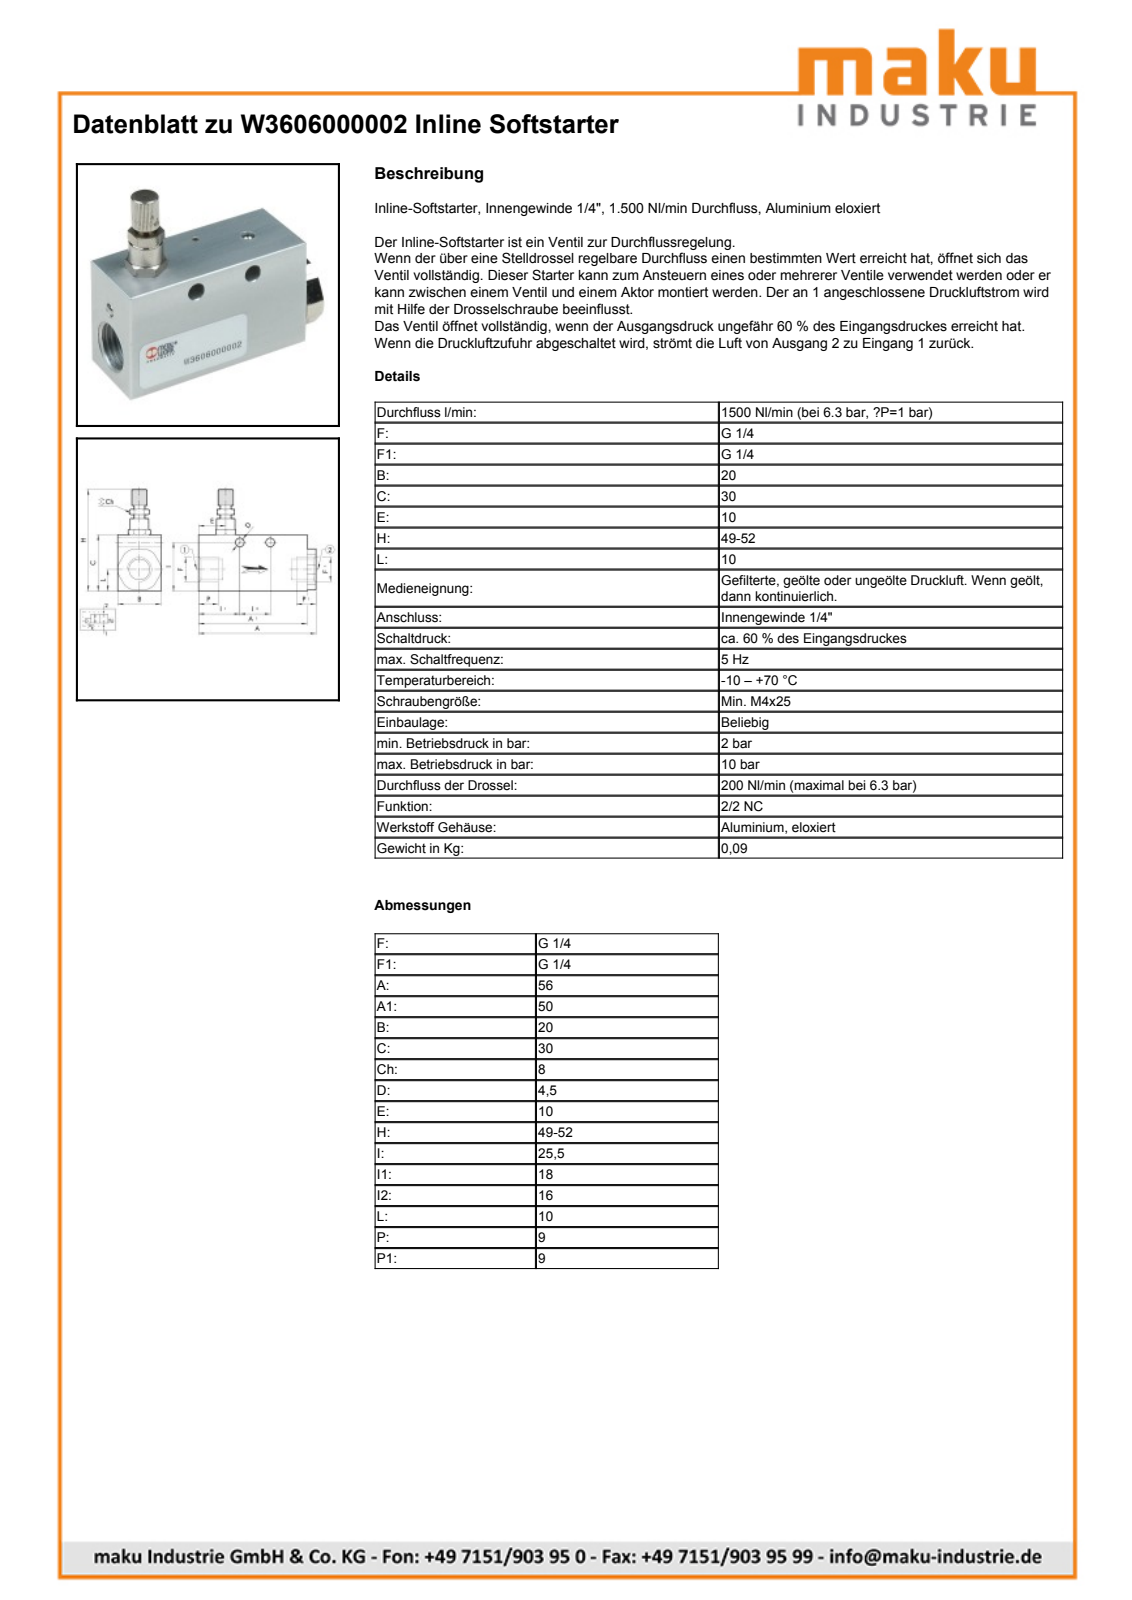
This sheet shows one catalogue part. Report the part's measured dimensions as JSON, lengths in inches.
{"part_name": "W360600000249", "step_written_by": "PARTsolutions (AUTOMOTIVE_DESIGN)", "units": "inches", "bodies": {"solids": 1, "faces": 61, "planar": 33, "cylindrical": 26, "other": 2}, "overall_size": [2.205, 1.929, 0.787], "volume_in3": 1.816, "surface_area_in2": 13.01, "round_holes": [[0.177, 2], [0.451, 1]], "round_bosses_or_shafts": [[0.335, 1], [0.272, 1], [0.197, 1]], "partial_cylinders_radius": [[0.177, 1], [0.201, 1], [0.392, 1]], "face_to_face_distances": [0.787, 1.181, 1.969, 0.433, 1.772, 0.236, 2.205, 0.748, 0.197, 1.535], "hole_center_spacings": [0.63]}
